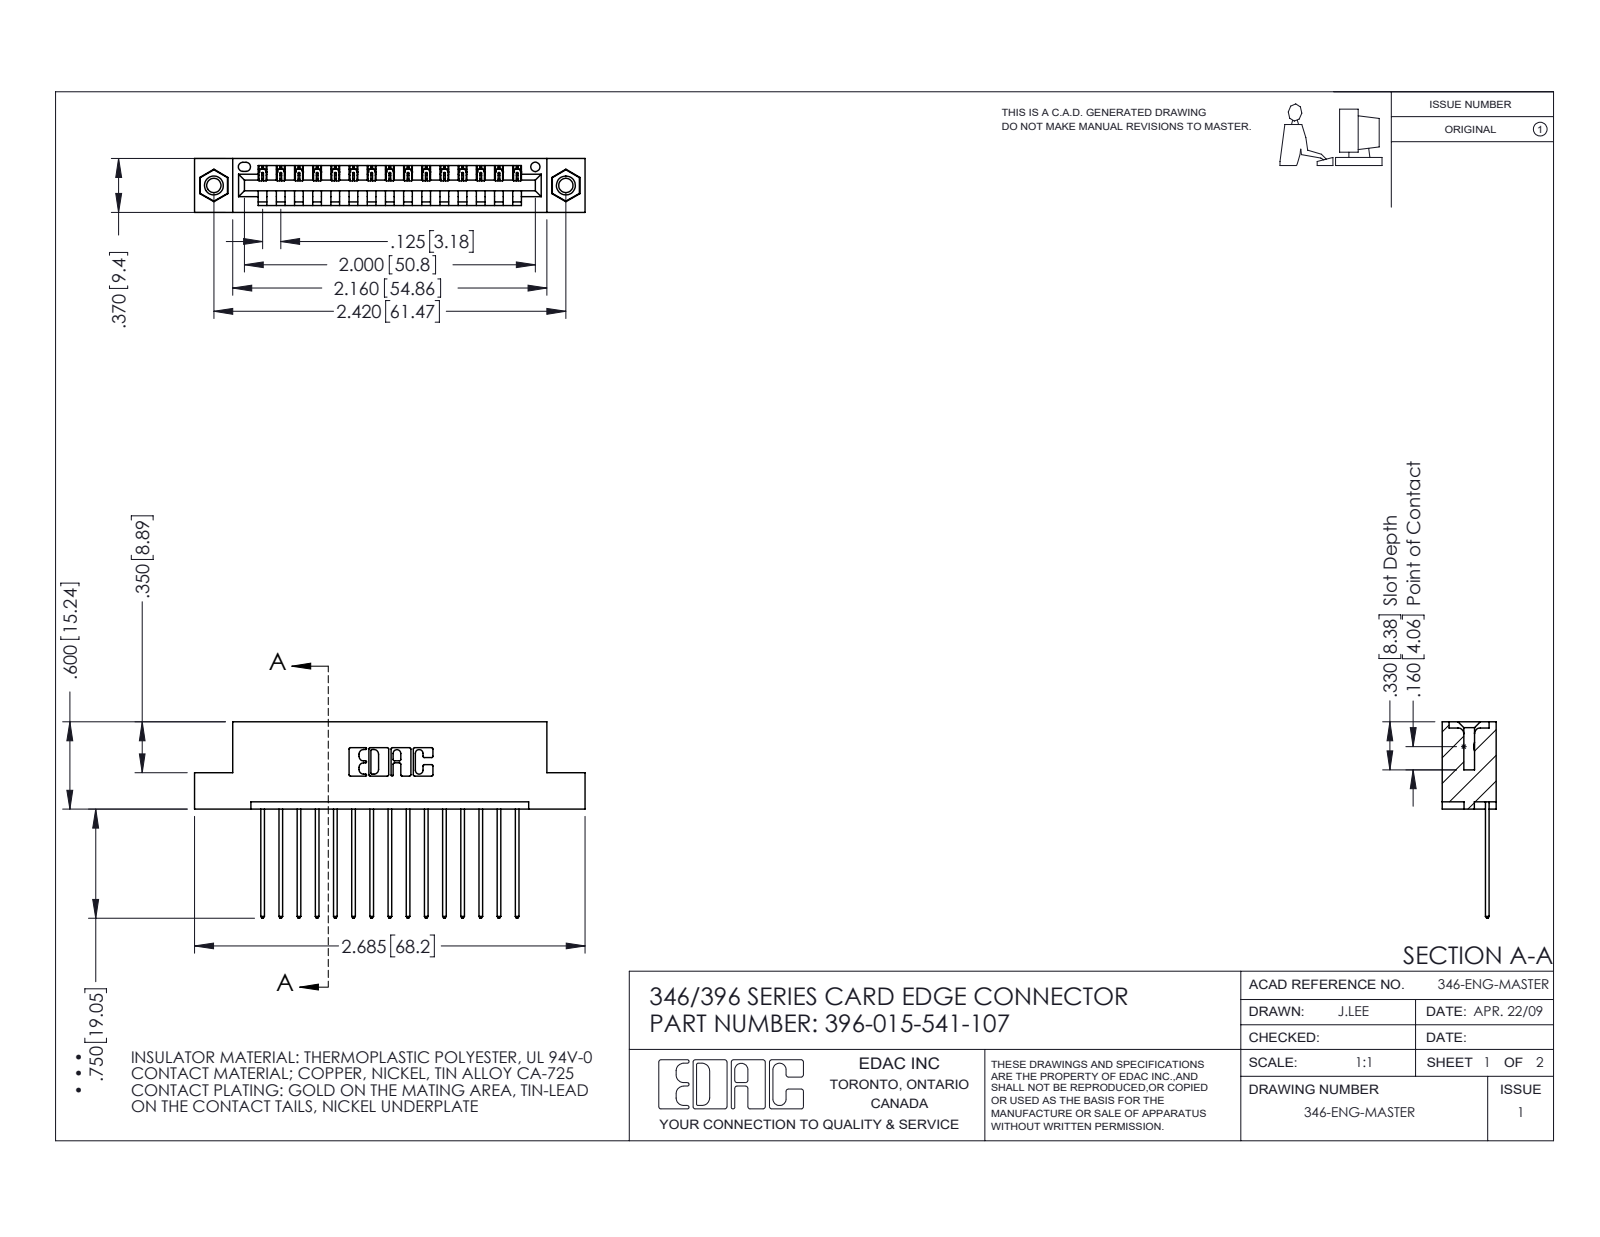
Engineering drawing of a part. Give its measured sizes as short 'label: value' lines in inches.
name: 346 Part_Flush Mounting Lugs - 0.156 Dia-TI; 396-015-541-107; 345-250-001_345-250-005-103; 345-292-001_345-293-141
written by: SolidWorks 2016 (CONFIG_CONTROL_DESIGN)
unit: in
bodies: 18 solids, 1052 faces (708 planar, 328 cylindrical, 16 other)
size: 2.685 × 1.35 × 0.37
volume: 0.389 in³; area: 12.42 in²
holes: 2× ⌀0.098, 2× ⌀0.125, 2× ⌀0.156, 1× ⌀0.064
bosses: 2× ⌀0.155
rounds: 30× R0.006, 30× R0.01, 22× R0.01, 6× R0.007, 6× R0.031, 3× R0.026, 2× R0.031, 2× R0.04
face distances: 0.048, 0.322, 0.25, 0.37, 0.072, 0.298, 0.025, 0.148, 0.222, 0.1
hole spacings: 0.246, 2.213, 2.42
